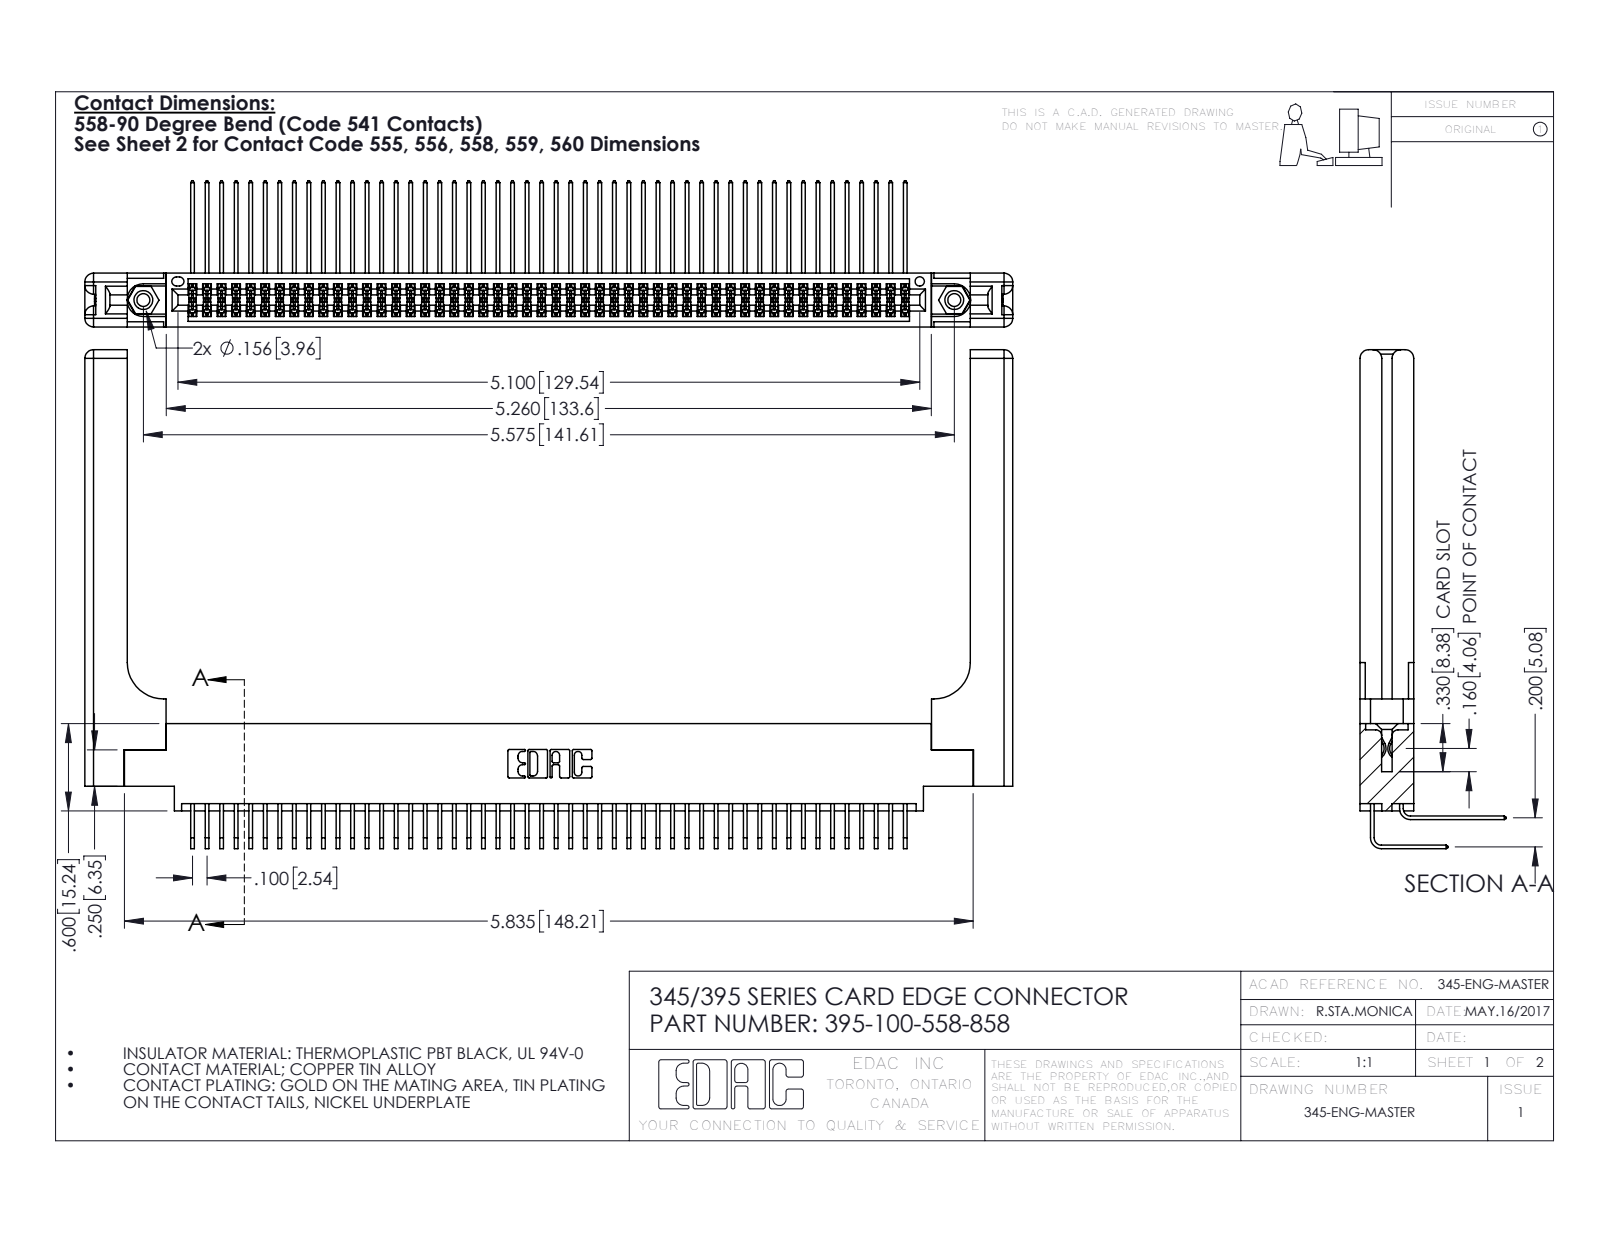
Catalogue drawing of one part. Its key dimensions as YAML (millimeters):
part_name: "395-100-558-858; 345-292-001_558 Tail - 2; 345-250-001_345-250-001-102; 345-220-058_345-220-058 (+2 more)"
step_written_by: "SolidWorks 2016 (CONFIG_CONTROL_DESIGN)"
units: millimeters
bodies: {solids: 105, faces: 5586, planar: 3732, cylindrical: 1794, other: 60}
overall_size: [162, 87.1, 25.5]
volume: 24740
surface_area: 32130
round_holes:
  - {diameter: 2.3, count: 2}
  - {diameter: 3.2, count: 2}
  - {diameter: 4, count: 2}
  - {diameter: 1.6, count: 1}
round_bosses_or_shafts:
  - {diameter: 3.9, count: 2}
partial_cylinders:
  - {radius: 0.2, count: 151}
  - {radius: 0.3, count: 22}
  - {radius: 1.5, count: 16}
  - {radius: 0.2, count: 6}
  - {radius: 0.8, count: 6}
  - {radius: 0.7, count: 3}
  - {radius: 0.4, count: 2}
  - {radius: 0.5, count: 2}
face_to_face_distances: [1.8, 9.4, 7.6, 5.1, 2.5, 6.9, 0.6, 5.7, 4.4, 3.8]
hole_center_spacings: [6.9, 135.6, 141.6]
